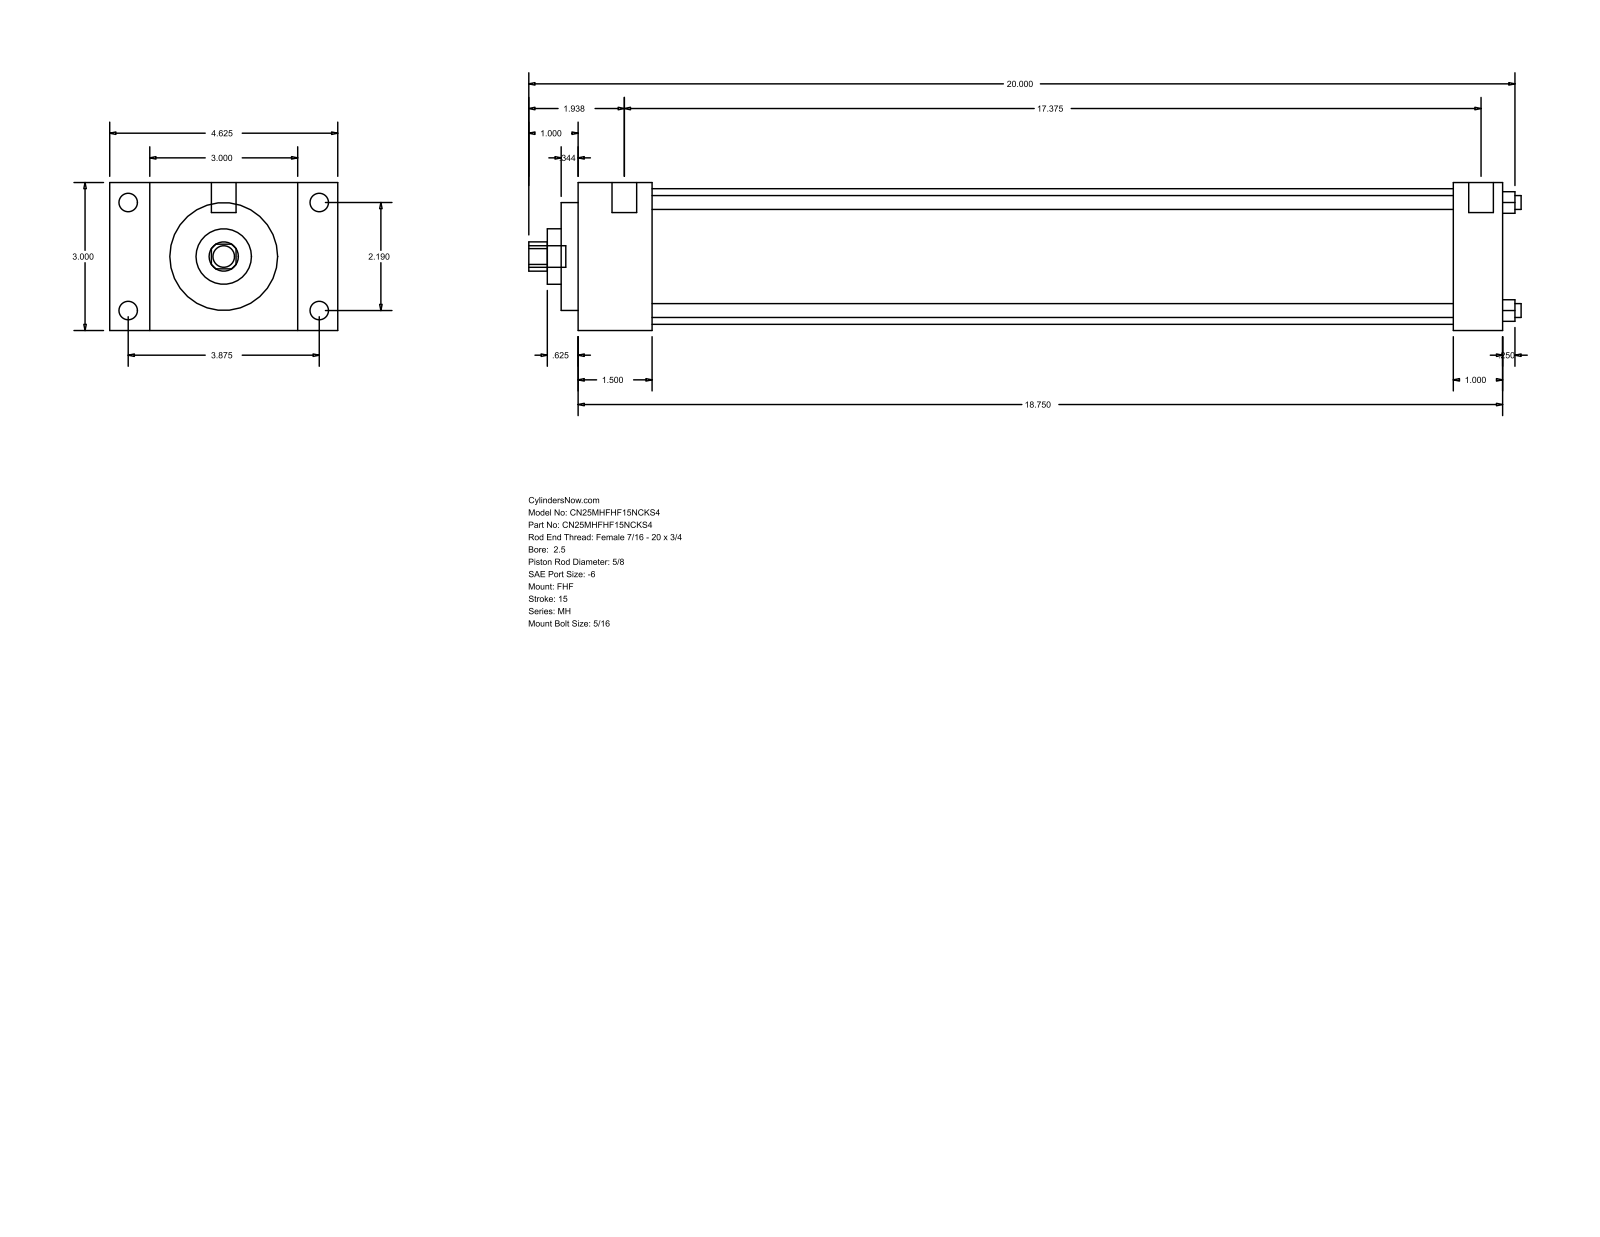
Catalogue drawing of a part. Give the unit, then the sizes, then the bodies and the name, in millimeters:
Units: millimetres
Overall size (bounding box): 511.18 × 117.47 × 76.2
Round holes (diameter × count): ⌀7.14 ×4, ⌀15.88 ×1, ⌀28.57 ×1, ⌀55.55 ×1, ⌀69.85 ×1
Round bosses / shafts (diameter × count): ⌀9.53 ×4, ⌀5.56 ×4, ⌀12.7 ×2, ⌀11.11 ×1
Partial cylindrical surfaces — rounded edges, fillets, slot ends (radius × count): R7.54 ×1
Main face-to-face distances: 76.2, 476.25, 38.1, 438.15, 20.64, 96.84, 117.48, 25.4, 450.85, 412.75
Hole centre spacings: 39.33, 55.62, 78.66
Bodies: 0 solids, 90 faces (61 planar, 29 cylindrical, 0 other)
Part name (STEP PRODUCT): MH_FHF__0250_0.625
STEP written by: GSSL Pune (CONFIG_CONTROL_DESIGN)
